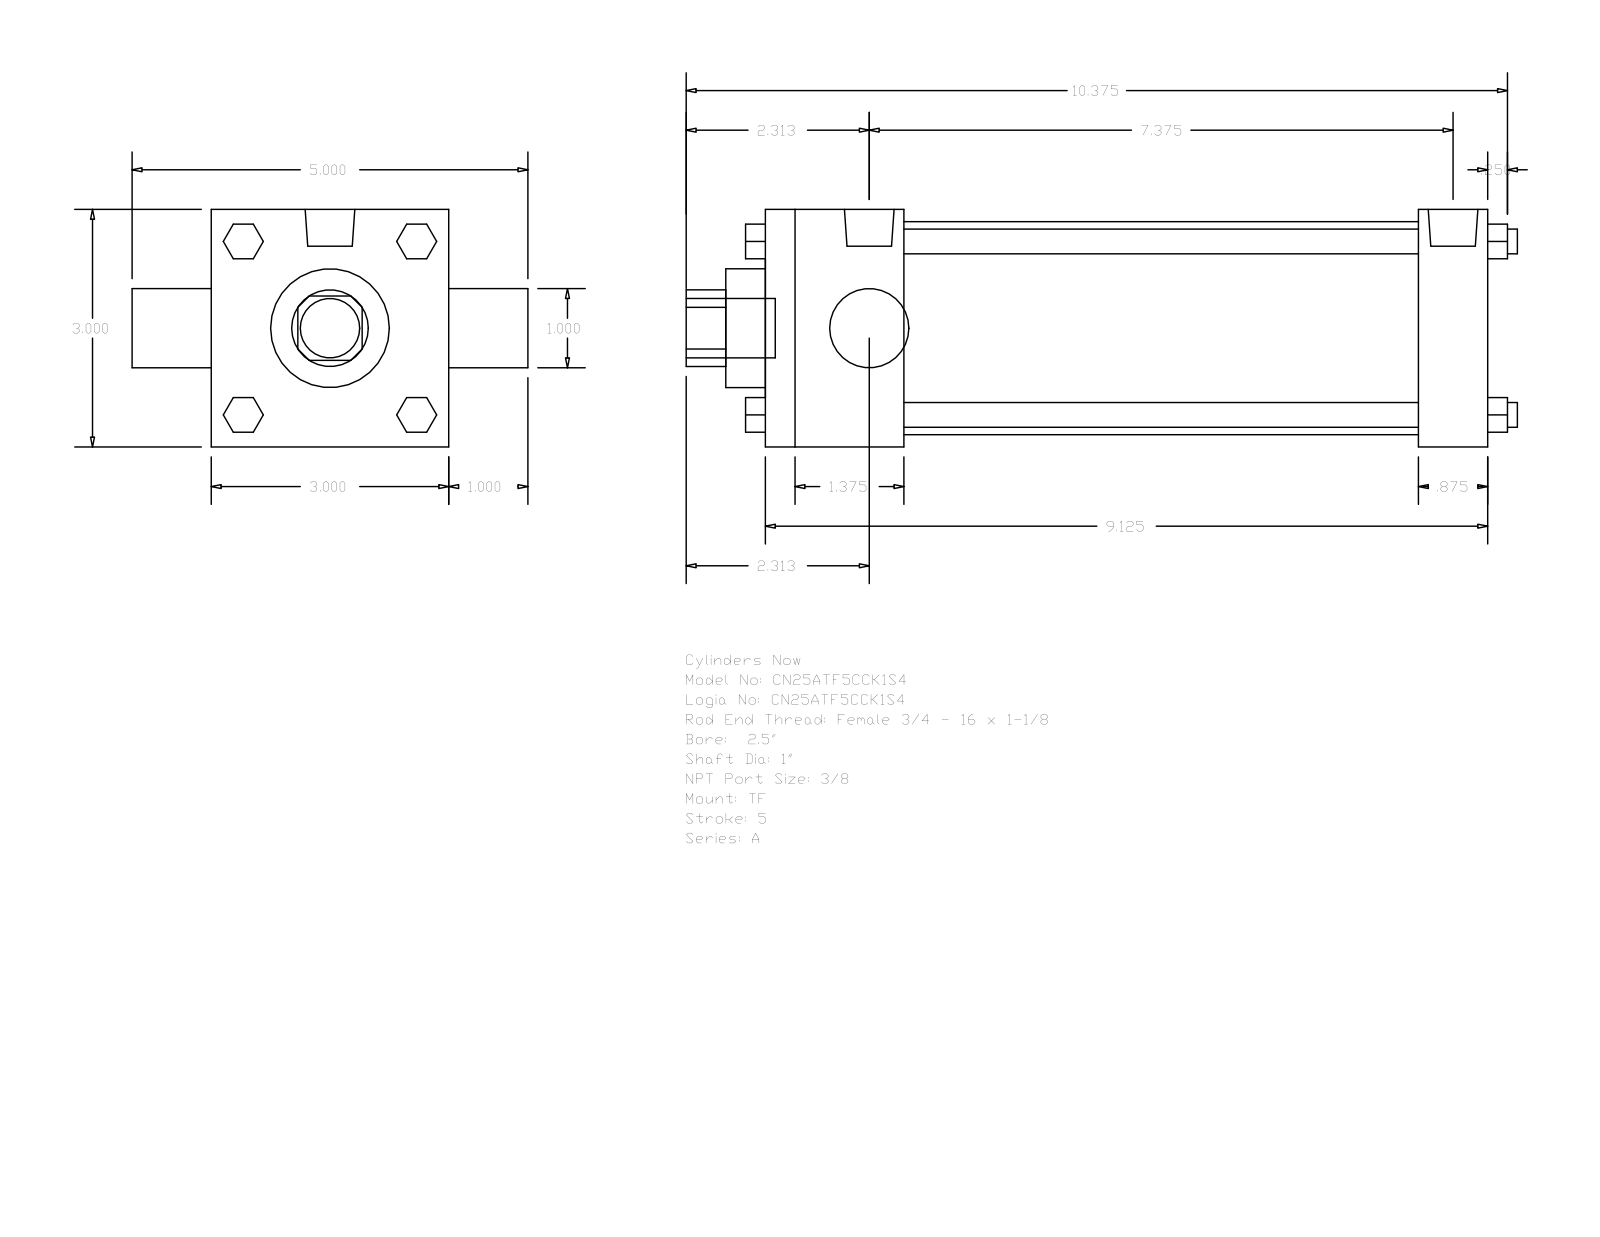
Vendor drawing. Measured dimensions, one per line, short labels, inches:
name: A_TF__0250_1
written by: GSSL Pune (CONFIG_CONTROL_DESIGN)
unit: in
bodies: 0 solids, 120 faces (92 planar, 28 cylindrical, 0 other)
size: 10.5 × 5 × 3
holes: 2× ⌀1, 1× ⌀1.5, 1× ⌀2.69
bosses: 4× ⌀0.313, 3× ⌀0.219, 2× ⌀0.627, 1× ⌀0.75
rounds: 1× R0.484
face distances: 3, 9.125, 1.75, 8.25, 6.5, 7.375, 0.875, 1, 4, 0.5
